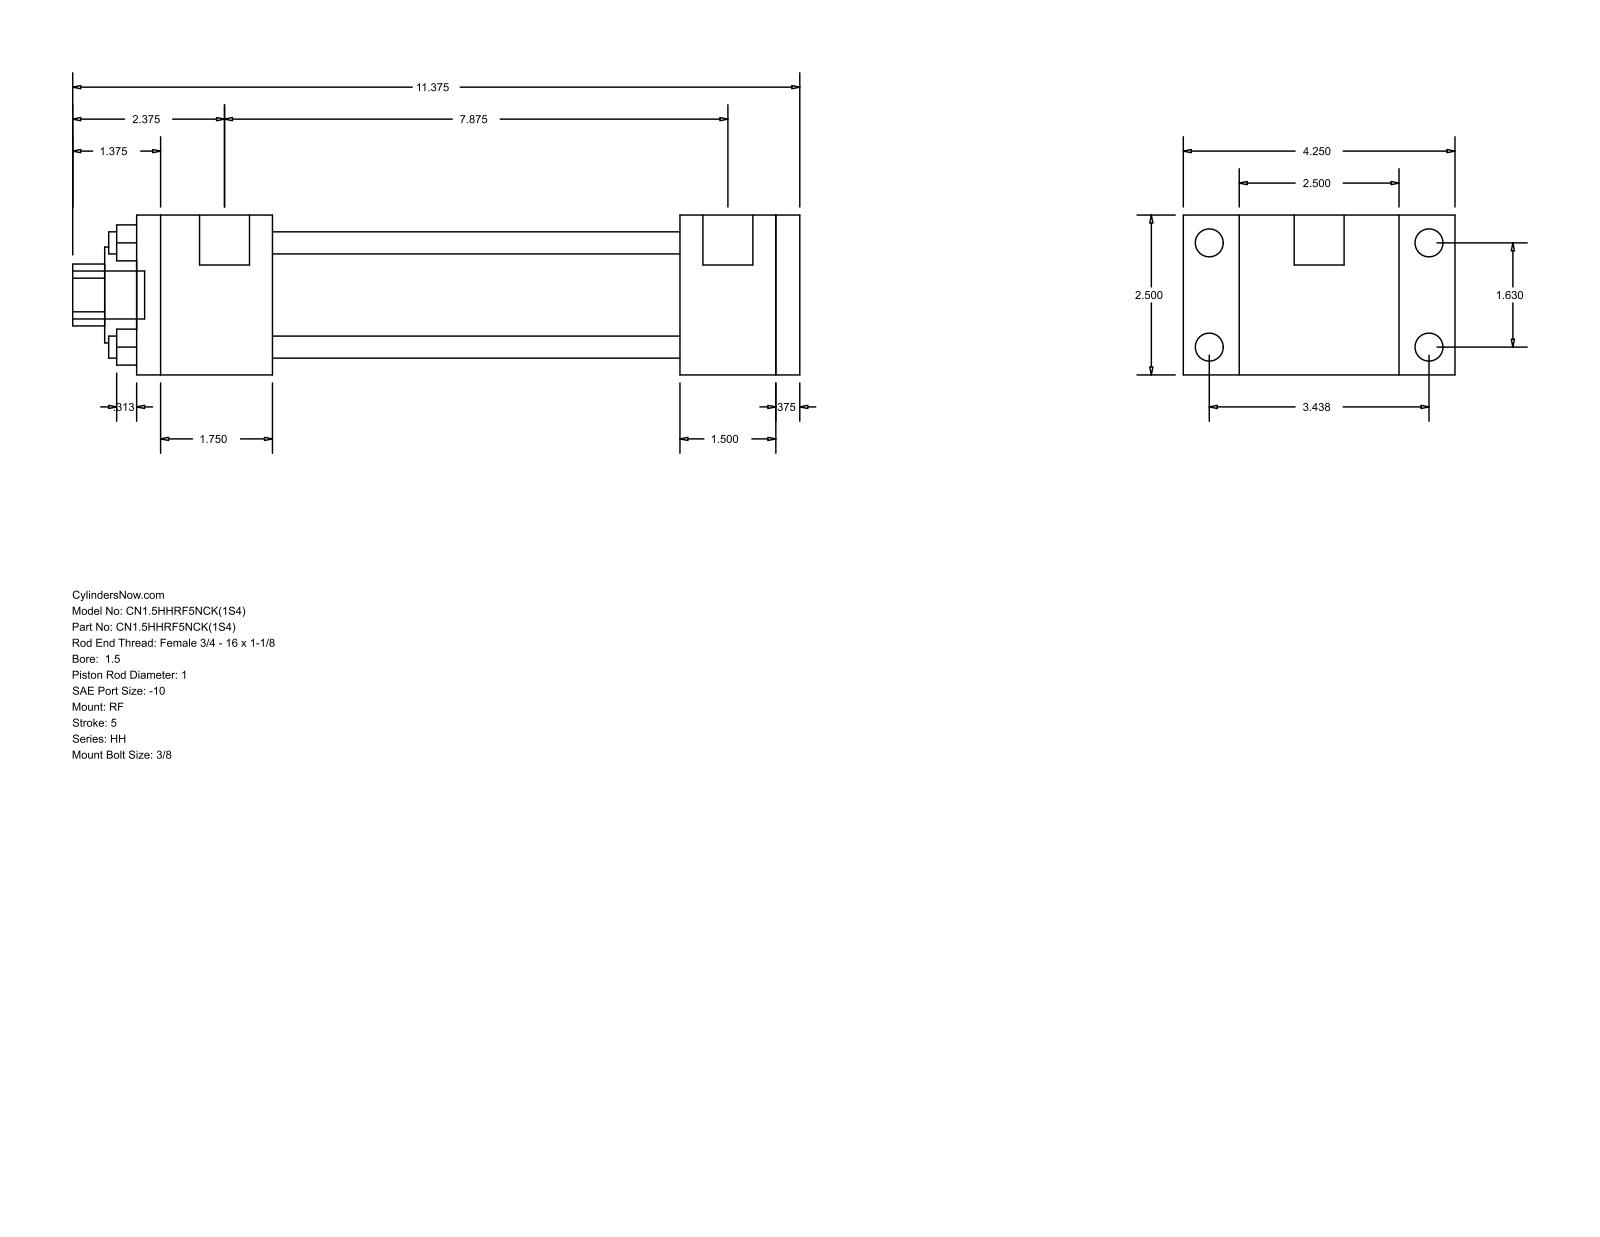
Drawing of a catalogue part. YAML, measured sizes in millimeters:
part_name: "HH_RF__0150_1"
step_written_by: "GSSL Pune (CONFIG_CONTROL_DESIGN)"
units: millimeters
bodies: {solids: 0, faces: 92, planar: 64, cylindrical: 28, other: 0}
overall_size: [288.93, 107.95, 63.5]
round_holes:
  - {diameter: 8.76, count: 4}
  - {diameter: 25.4, count: 1}
  - {diameter: 38.1, count: 1}
  - {diameter: 44.45, count: 1}
round_bosses_or_shafts:
  - {diameter: 11.13, count: 4}
  - {diameter: 5.56, count: 4}
  - {diameter: 19.84, count: 2}
  - {diameter: 19.05, count: 1}
partial_cylinders:
  - {radius: 12.29, count: 1}
face_to_face_distances: [63.5, 9.53, 161.92, 200.02, 209.55, 38.1, 47.63, 53.98, 215.9, 254]
hole_center_spacings: [29.27, 41.4, 58.55]
